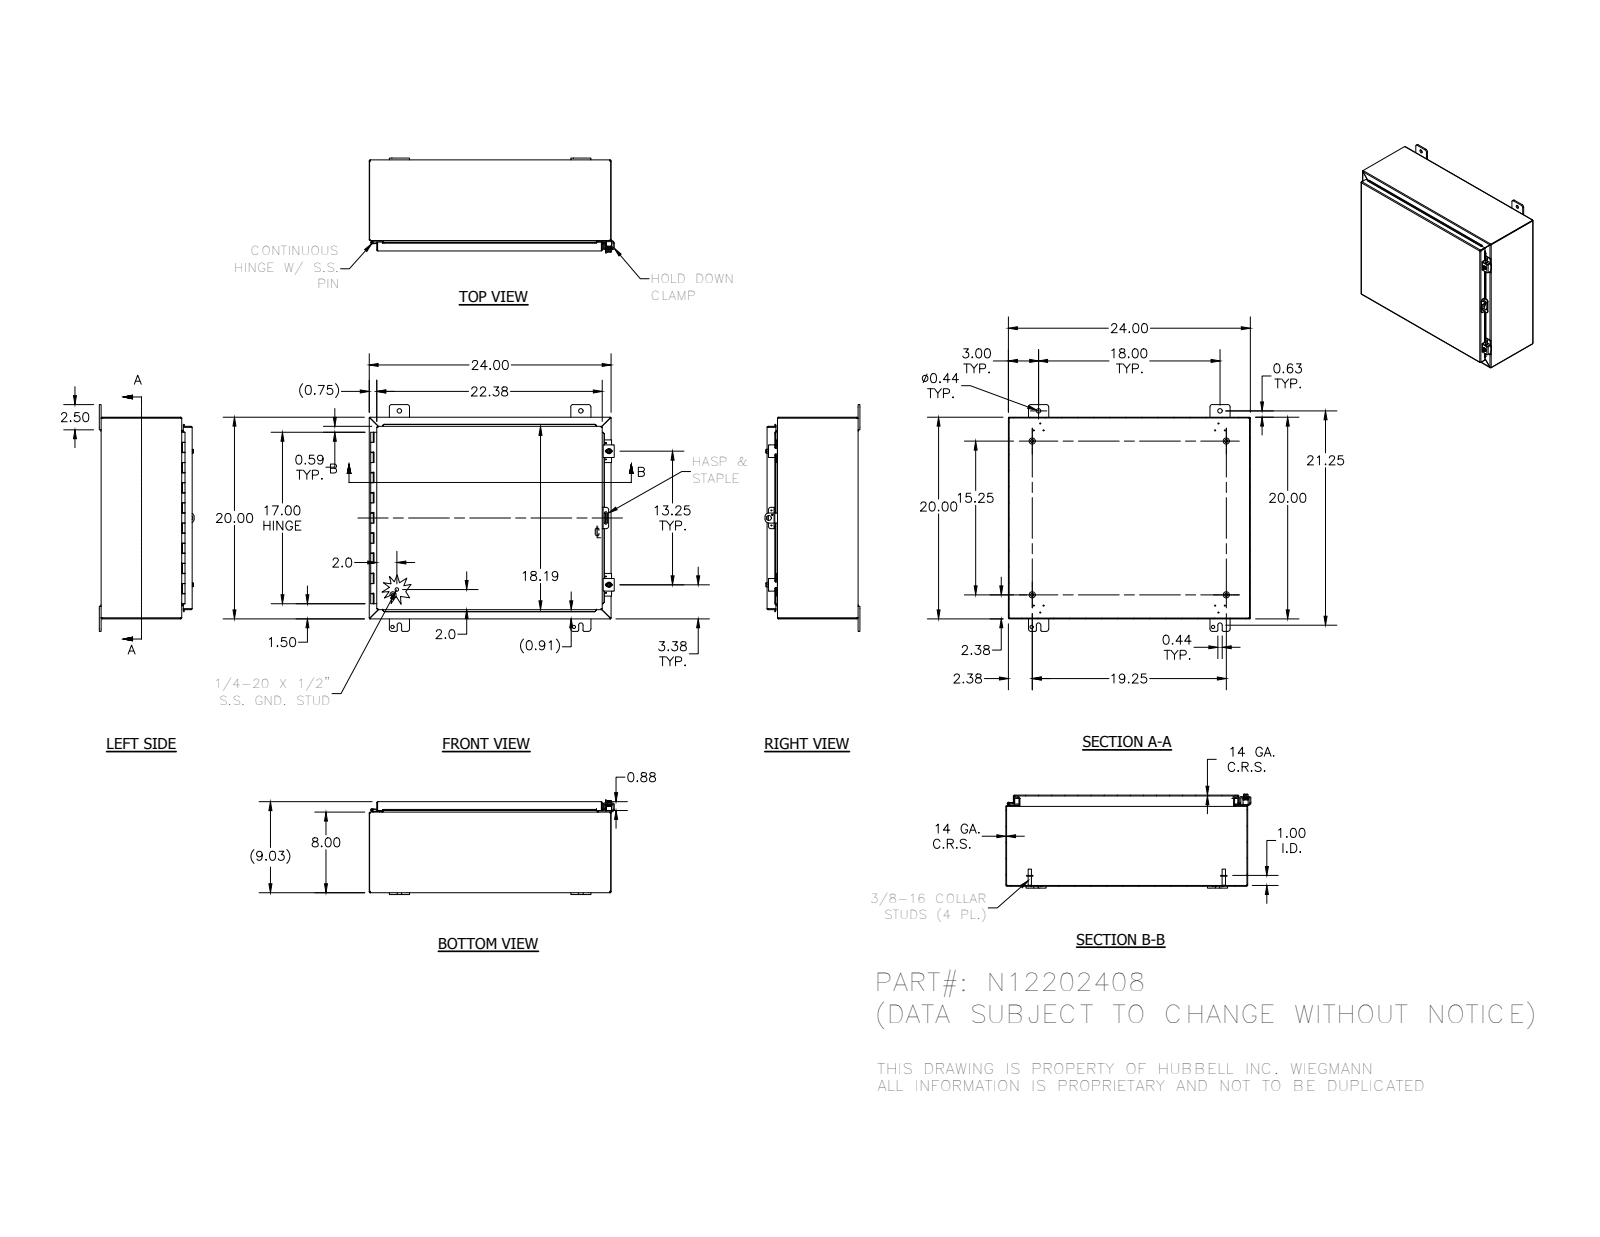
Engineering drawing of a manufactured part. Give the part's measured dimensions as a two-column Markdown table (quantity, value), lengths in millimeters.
| quantity | value |
| --- | --- |
| part name | N12202408; 34840; 38420; N12202408BKP (+8 more) |
| STEP written by | Autodesk Inventor 2012 (AUTOMOTIVE_DESIGN) |
| units | millimeters |
| bodies | 27 solids, 948 faces (511 planar, 320 cylindrical, 117 other) |
| overall size | 617.5 × 571.5 × 239 |
| volume | 2 486 000 mm³ |
| surface area | 2 550 000 mm² |
| round holes (diameter × count) | 3 × 12, 2.8 × 7, 8 × 4, 11.1 × 4, 5.4 × 2, 7.1 × 2, 7.6 × 2, 3.2 × 1, 4 × 1, 12.7 × 1 |
| round bosses / shafts (diameter × count) | 15.9 × 4, 8.4 × 4, 6.4 × 4, 13.2 × 2, 12.7 × 2, 8.9 × 2, 2.9 × 2, 8.6 × 1 |
| partial cylindrical surfaces (radius × count) | 0.8 × 27, 1.6 × 25, 3.2 × 25, 6.4 × 25, 0.8 × 23, 2.7 × 23, 1.8 × 8, 2.5 × 4 |
| main face-to-face distances | 1.9, 227.6, 225.7, 229.4, 506.1, 607.7, 201.3, 26.2, 508, 504.2 |
| hole center spacings | 457.2, 19.3, 21.3, 23.9, 24.6, 40.5, 50.7, 441.2 |
